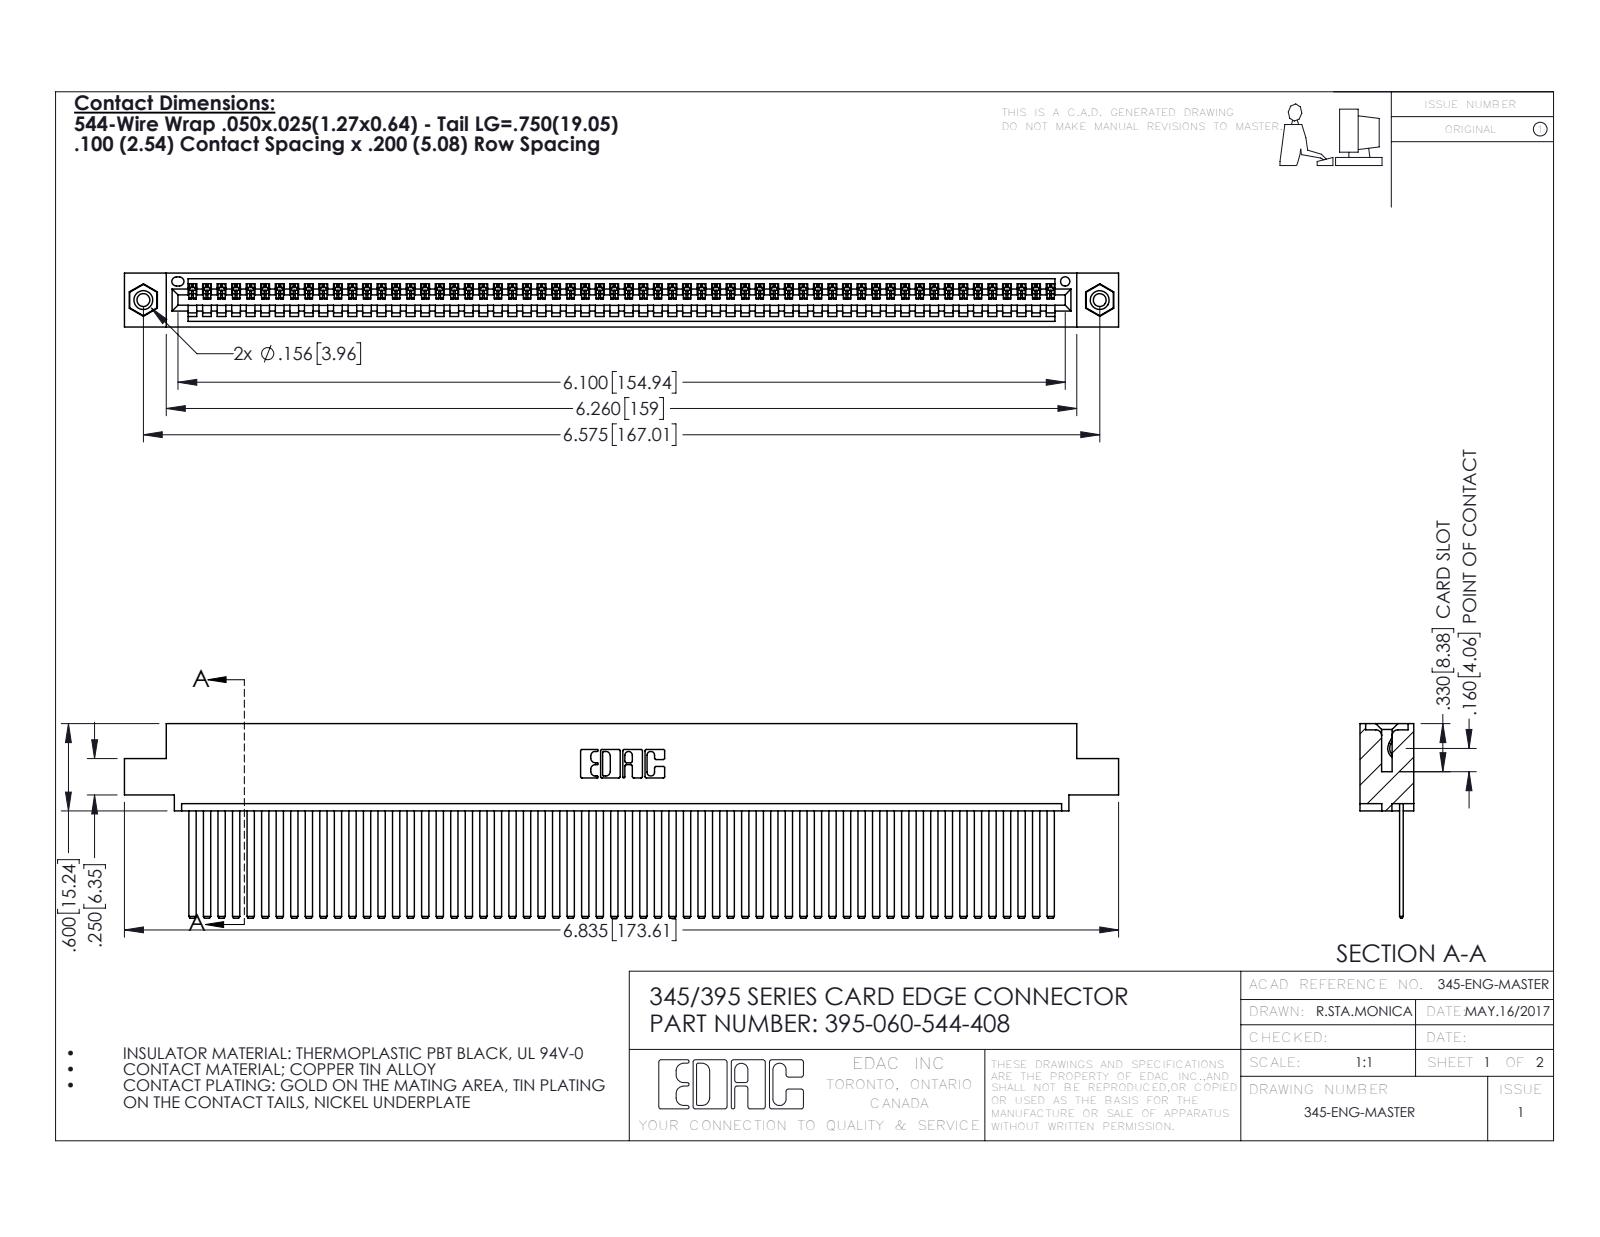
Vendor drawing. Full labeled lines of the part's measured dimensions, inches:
Part name (STEP PRODUCT): 395-060-544-408; 345-250-001_345-250-003-102; 345 Part_0.110 Offset - 0.156 Dia-TI; 345-292-001_345-293-144
STEP written by: SolidWorks 2016 (CONFIG_CONTROL_DESIGN)
Units: inches
Bodies: 63 solids, 3310 faces (2276 planar, 1018 cylindrical, 16 other)
Overall size (bounding box): 6.835 × 1.337 × 0.37
Volume: 1.053 in³ · Surface area: 39.31 in²
Round holes (diameter × count): ⌀0.089 ×2, ⌀0.125 ×2, ⌀0.156 ×2, ⌀0.064 ×1
Round bosses / shafts (diameter × count): ⌀0.155 ×2
Partial cylindrical surfaces — rounded edges, fillets, slot ends (radius × count): R0.006 ×120, R0.01 ×22, R0.007 ×6, R0.031 ×6, R0.026 ×3, R0.031 ×2, R0.04 ×2, R0.014 ×1
Main face-to-face distances: 0.072, 0.298, 0.025, 0.098, 0.272, 0.37, 0.2, 0.225, 0.149, 0.072
Hole centre spacings: 0.27, 6.339, 6.575
